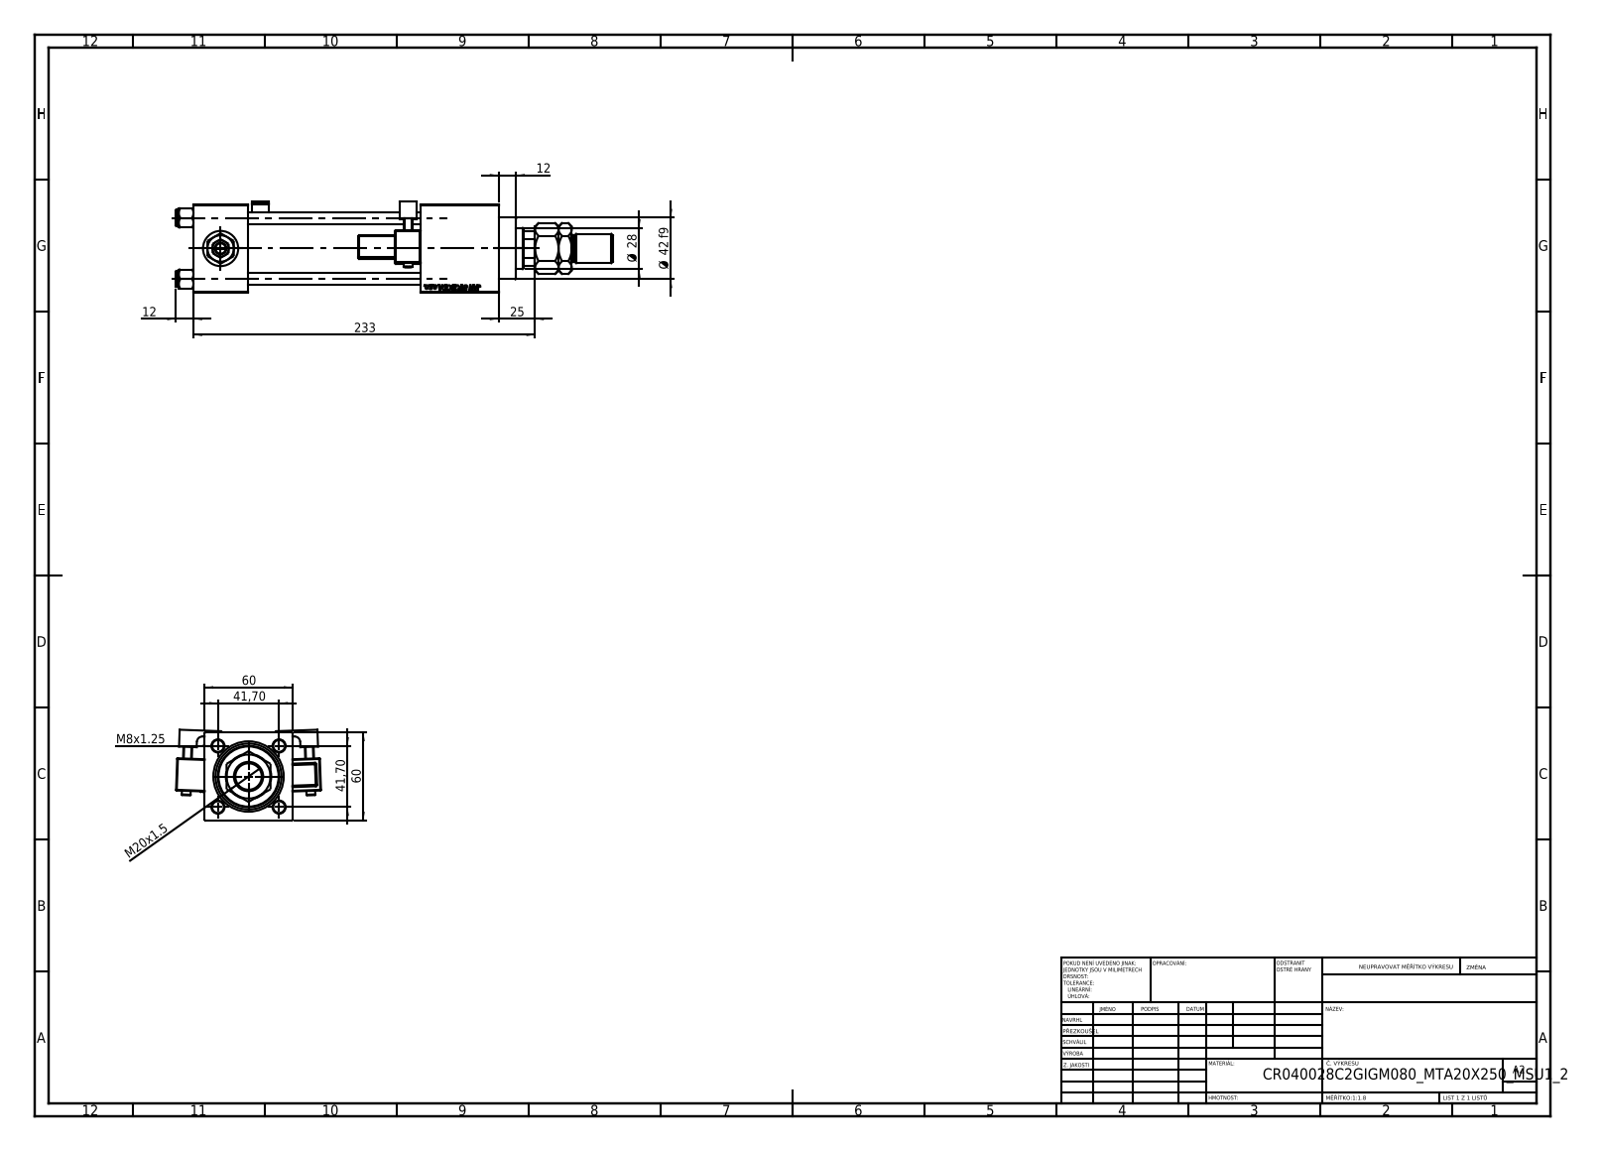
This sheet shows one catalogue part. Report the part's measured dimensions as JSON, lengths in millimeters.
{"part_name": "V215CR_C_Body; V215CR_MSU; V215CR_VCP_C; MTA (+4 more)", "step_written_by": "SolidWorks 2019 (CONFIG_CONTROL_DESIGN)", "units": "millimeters", "bodies": {"solids": 15, "faces": 1405, "planar": 623, "cylindrical": 158, "other": 624}, "overall_size": [298, 98.85, 61.9], "volume_mm3": 564900, "surface_area_mm2": 158549, "round_holes": [[8, 4], [7, 2], [16.66, 2], [24, 2], [18.5, 1], [28, 1], [31, 1], [40, 1], [45, 1]], "round_bosses_or_shafts": [[11, 4], [6, 2], [46, 1], [42, 1], [20, 1], [18, 1]], "partial_cylinders_radius": [[0.5, 48], [1, 2], [2.5, 2], [4, 2], [13.5, 1]], "face_to_face_distances": [60, 37, 155, 118, 53, 15, 179.3, 142.3, 24.3, 208], "hole_center_spacings": [29.49, 41.7, 58.97]}
